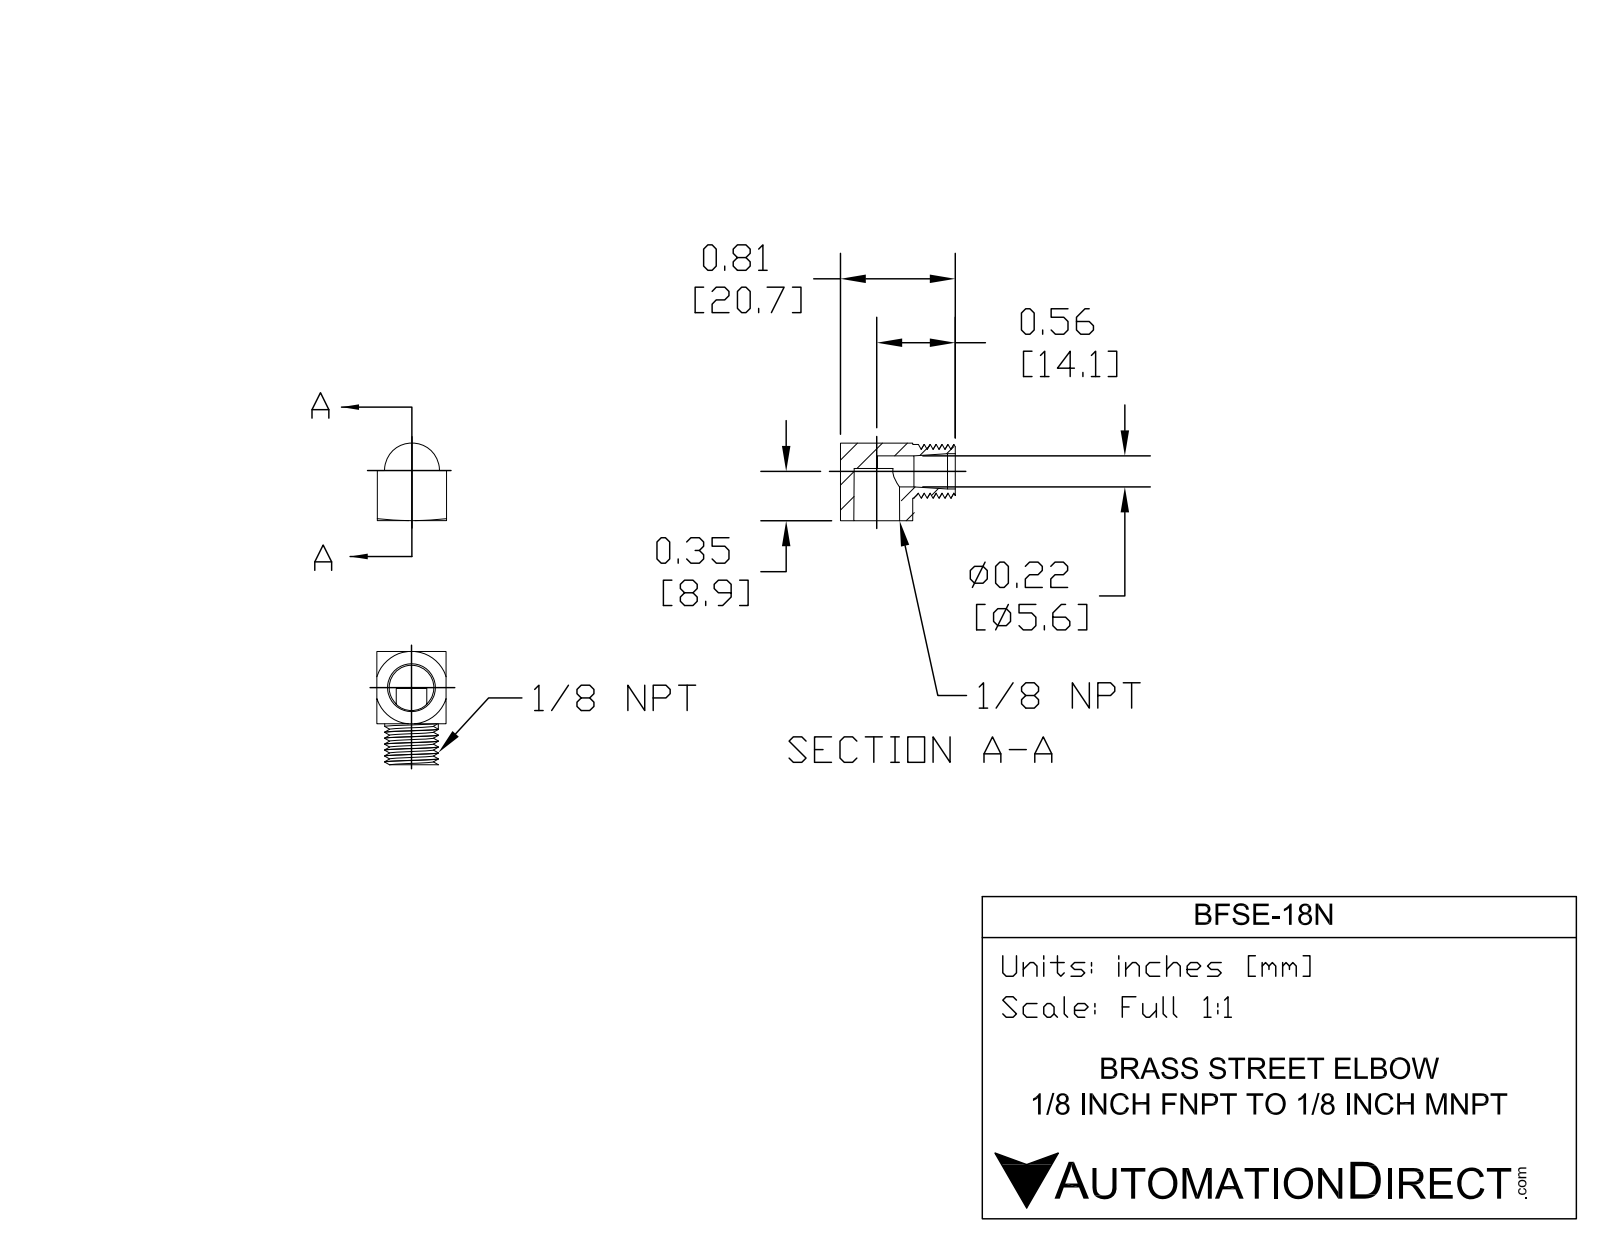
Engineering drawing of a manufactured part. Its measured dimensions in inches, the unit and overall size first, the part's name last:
Units: inches
Overall size (bounding box): 0.802 × 0.55 × 0.49
Round holes (diameter × count): ⌀0.22 ×1, ⌀0.25 ×1
Round bosses / shafts (diameter × count): ⌀0.38 ×1
Partial cylindrical surfaces — rounded edges, fillets, slot ends (radius × count): R0.195 ×1
Main face-to-face distances: 0.49, 0.512, 0.355, 0.37, 0.015, 0.29, 0.802, 0.54, 0.25, 0.262
Volume: 0.097 in³ · Surface area: 2.641 in²
Bodies: 1 solid, 41 faces (11 planar, 19 cylindrical, 11 other)
Part name (STEP PRODUCT): BFSE-18N
STEP written by: SolidWorks 2015 (CONFIG_CONTROL_DESIGN)
